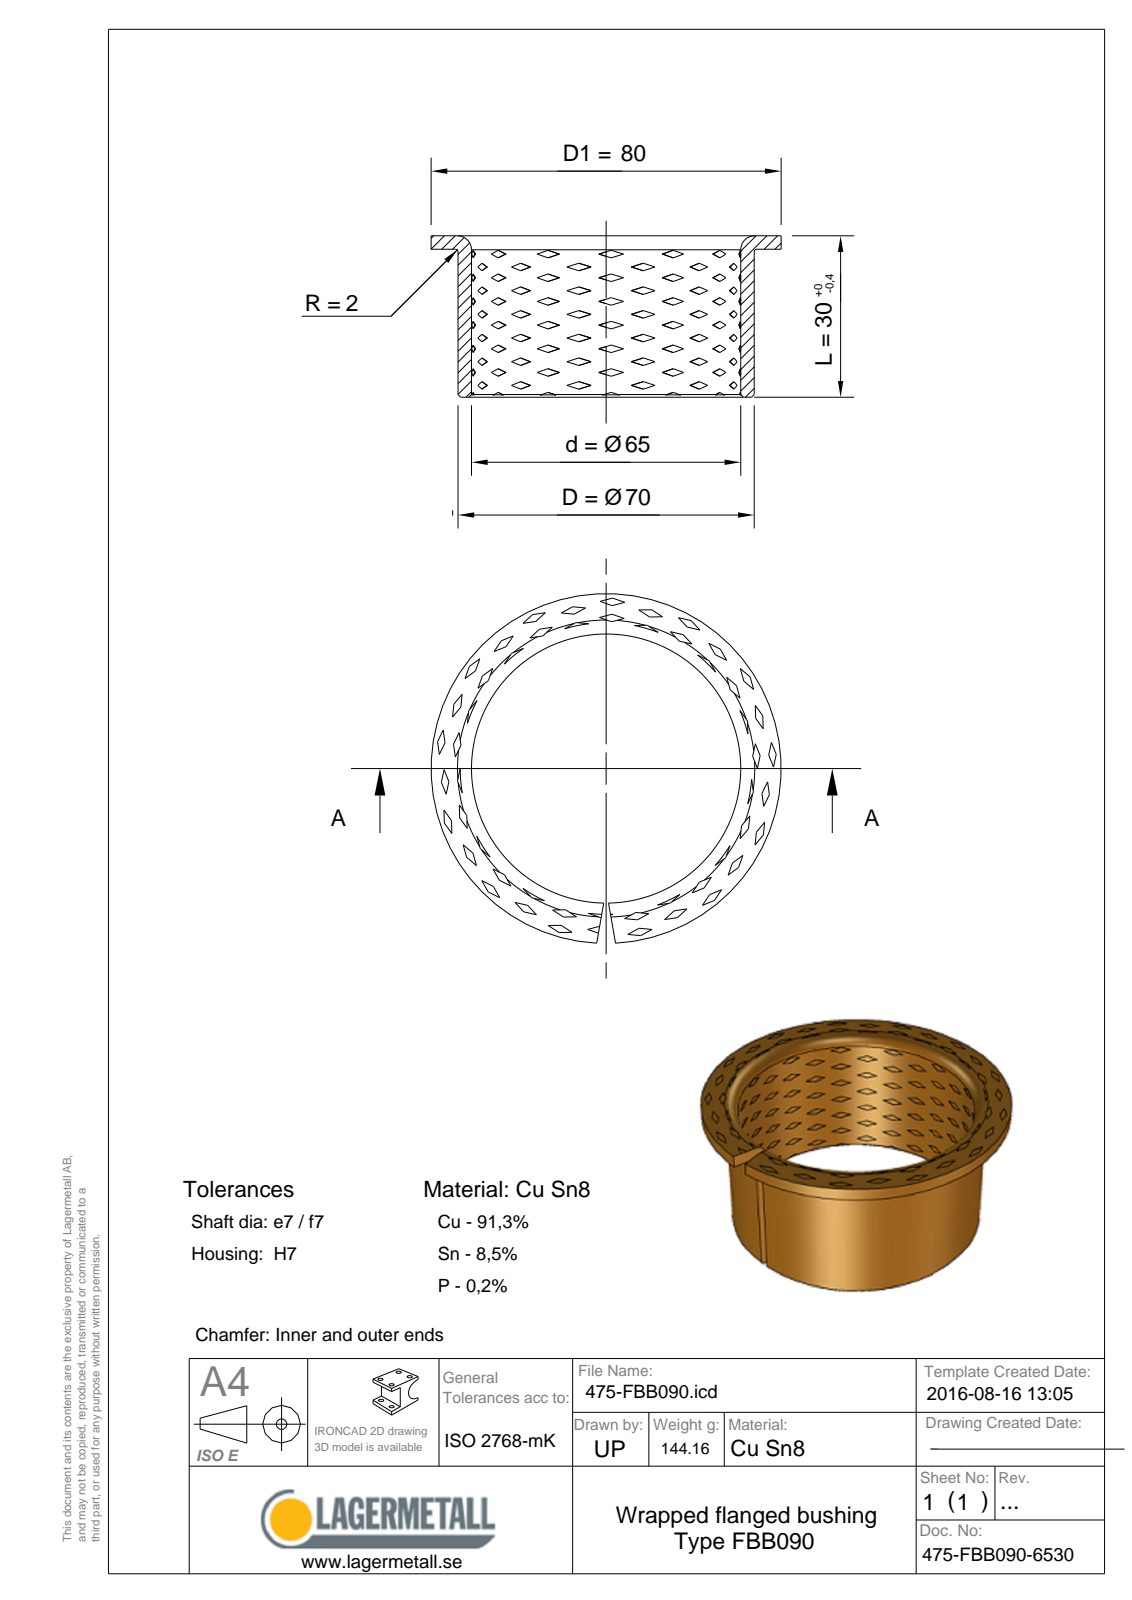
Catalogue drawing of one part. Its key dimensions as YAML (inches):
part_name: "475-FBB090-6530"
step_written_by: "Spatial InterOp 3D (CONFIG_CONTROL_DESIGN)"
units: inches
bodies: {solids: 1, faces: 12, planar: 5, cylindrical: 3, other: 4}
overall_size: [3.15, 3.148, 1.181]
volume: 1.086
surface_area: 24
round_holes:
  - {diameter: 2.559, count: 1}
round_bosses_or_shafts:
  - {diameter: 3.15, count: 1}
  - {diameter: 2.756, count: 1}
face_to_face_distances: [0.098, 1.083, 1.181]
